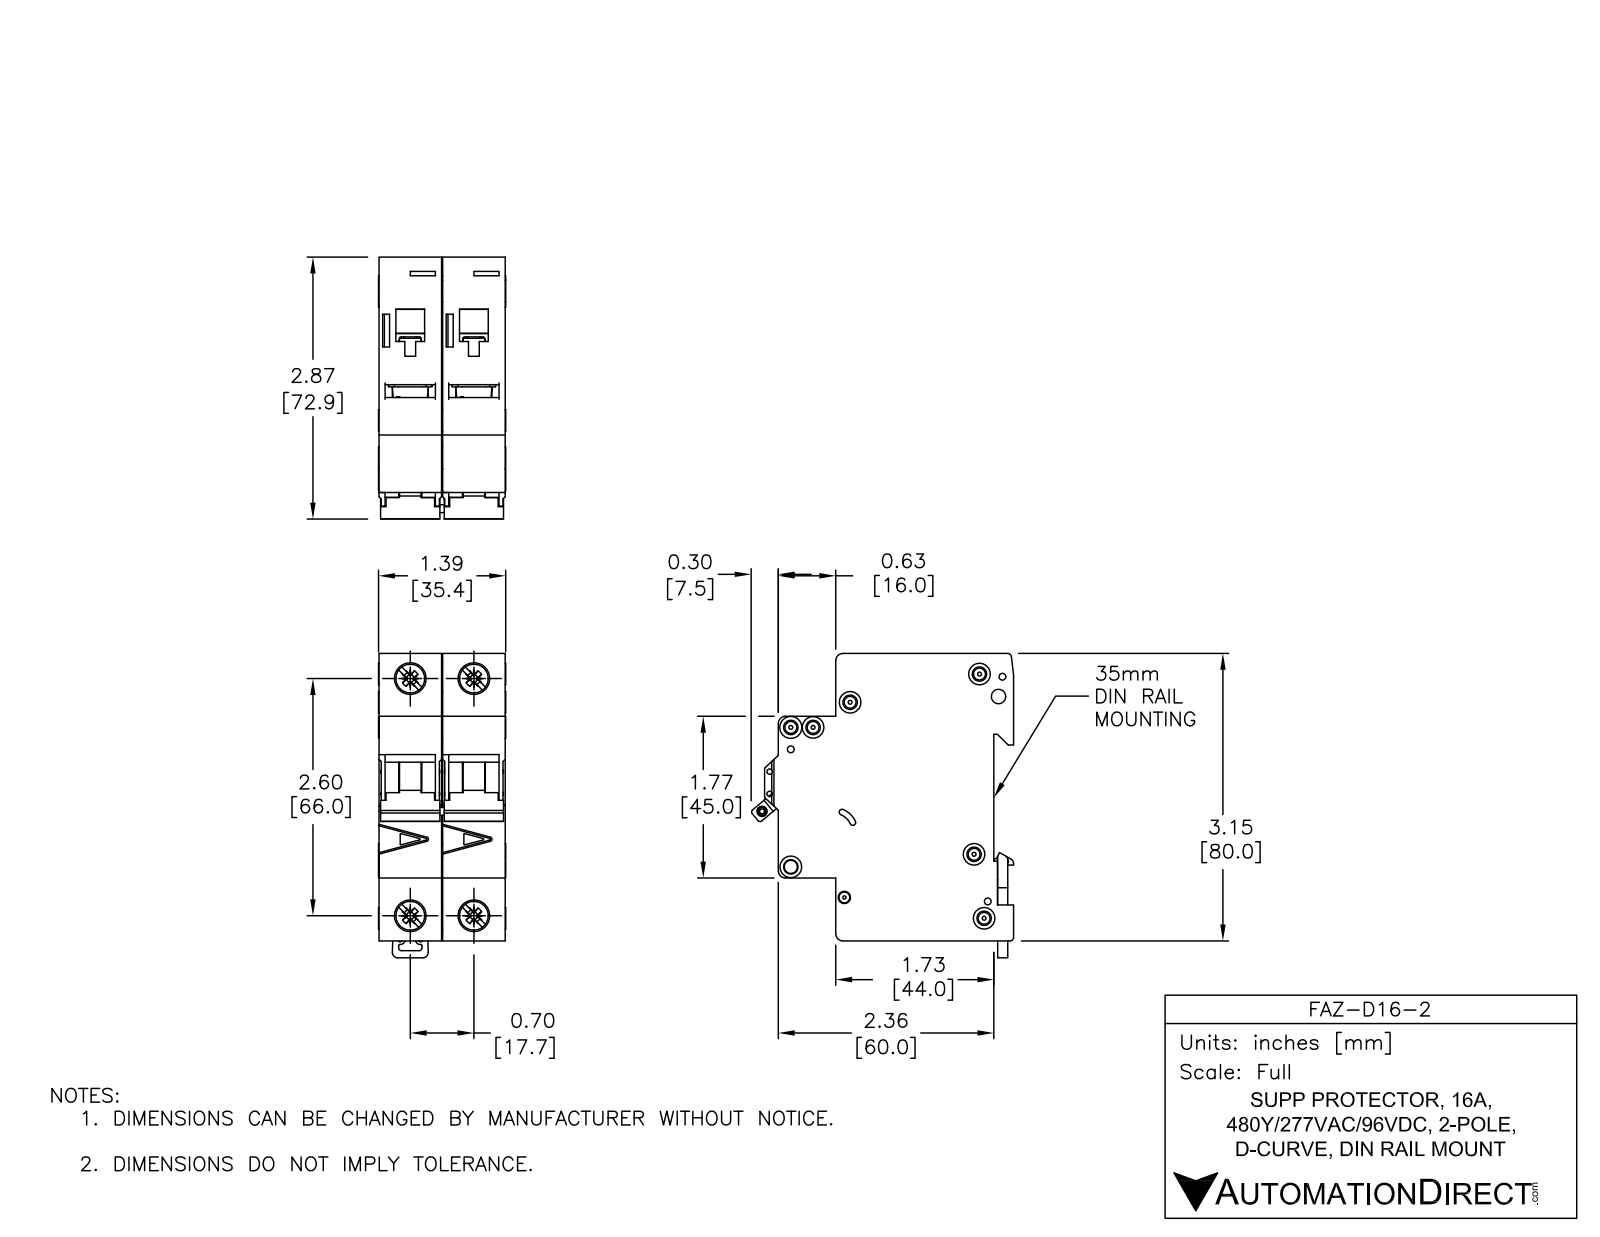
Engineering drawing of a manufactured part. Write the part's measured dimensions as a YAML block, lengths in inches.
part_name: "FAZ-D16-2"
step_written_by: "SolidWorks 2014 (AUTOMOTIVE_DESIGN)"
units: inches
bodies: {solids: 8, faces: 1104, planar: 466, cylindrical: 396, other: 242}
overall_size: [3.338, 2.876, 1.394]
volume: 9.142
surface_area: 60.14
round_holes:
  - {diameter: 0.142, count: 6}
  - {diameter: 0.075, count: 3}
  - {diameter: 0.043, count: 2}
  - {diameter: 0.059, count: 2}
  - {diameter: 0.157, count: 2}
  - {diameter: 0.281, count: 2}
  - {diameter: 0.323, count: 2}
  - {diameter: 0.085, count: 1}
  - {diameter: 0.087, count: 1}
  - {diameter: 0.1, count: 1}
  - {diameter: 0.13, count: 1}
  - {diameter: 0.134, count: 1}
round_bosses_or_shafts:
  - {diameter: 0.236, count: 4}
  - {diameter: 0.323, count: 2}
  - {diameter: 0.098, count: 2}
partial_cylinders:
  - {radius: 0.01, count: 49}
  - {radius: 0.02, count: 19}
  - {radius: 0.079, count: 10}
  - {radius: 0.008, count: 8}
  - {radius: 0.039, count: 8}
  - {radius: 0.031, count: 2}
  - {radius: 0.071, count: 2}
  - {radius: 0.118, count: 2}
face_to_face_distances: [0.697, 0.689, 1.386, 3.129, 0.217, 1.949, 1.732, 2.579, 2.362, 0.63]
hole_center_spacings: [0.244, 0.537, 0.697, 2.598, 2.69, 0.189, 0.204, 0.221]
